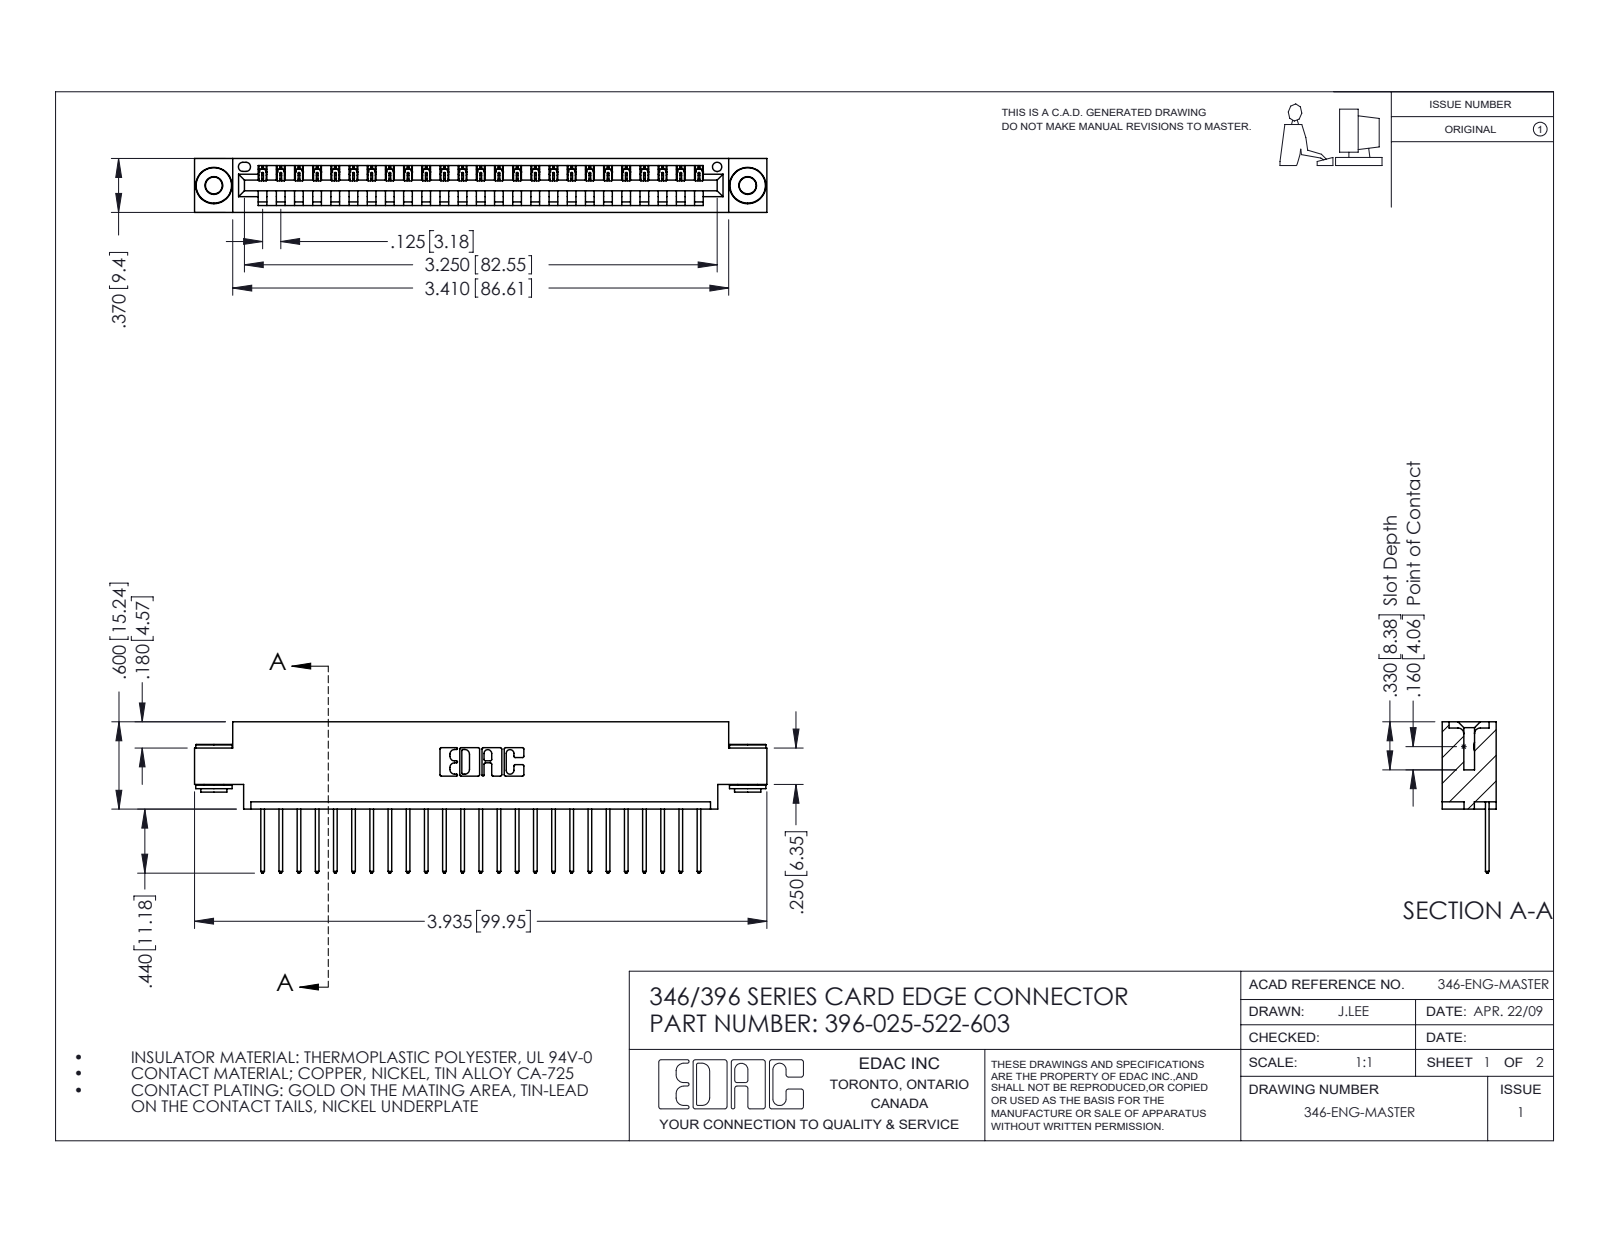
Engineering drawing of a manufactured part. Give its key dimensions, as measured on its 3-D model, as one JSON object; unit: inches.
{"part_name": "346 Part_0.170 Offset - 0.156 Dia-TH; 396-025-522-603; 345-292-001_345-293-122; 345-250-002_345-250-002-102", "step_written_by": "SolidWorks 2016 (CONFIG_CONTROL_DESIGN)", "units": "inches", "bodies": {"solids": 28, "faces": 1614, "planar": 1090, "cylindrical": 516, "other": 8}, "overall_size": [3.935, 1.04, 0.37], "volume_in3": 0.569, "surface_area_in2": 18.5, "round_holes": [[0.116, 2], [0.156, 2], [0.064, 1]], "round_bosses_or_shafts": [[0.25, 2], [0.18, 2], [0.136, 2]], "partial_cylinders_radius": [[0.006, 50], [0.01, 50], [0.01, 22], [0.007, 6], [0.031, 6], [0.026, 3], [0.031, 2], [0.04, 2]], "face_to_face_distances": [0.048, 0.322, 0.37, 0.25, 0.025, 0.072, 0.298, 0.148, 0.222, 0.1], "hole_center_spacings": [0.246, 3.462, 3.67]}
